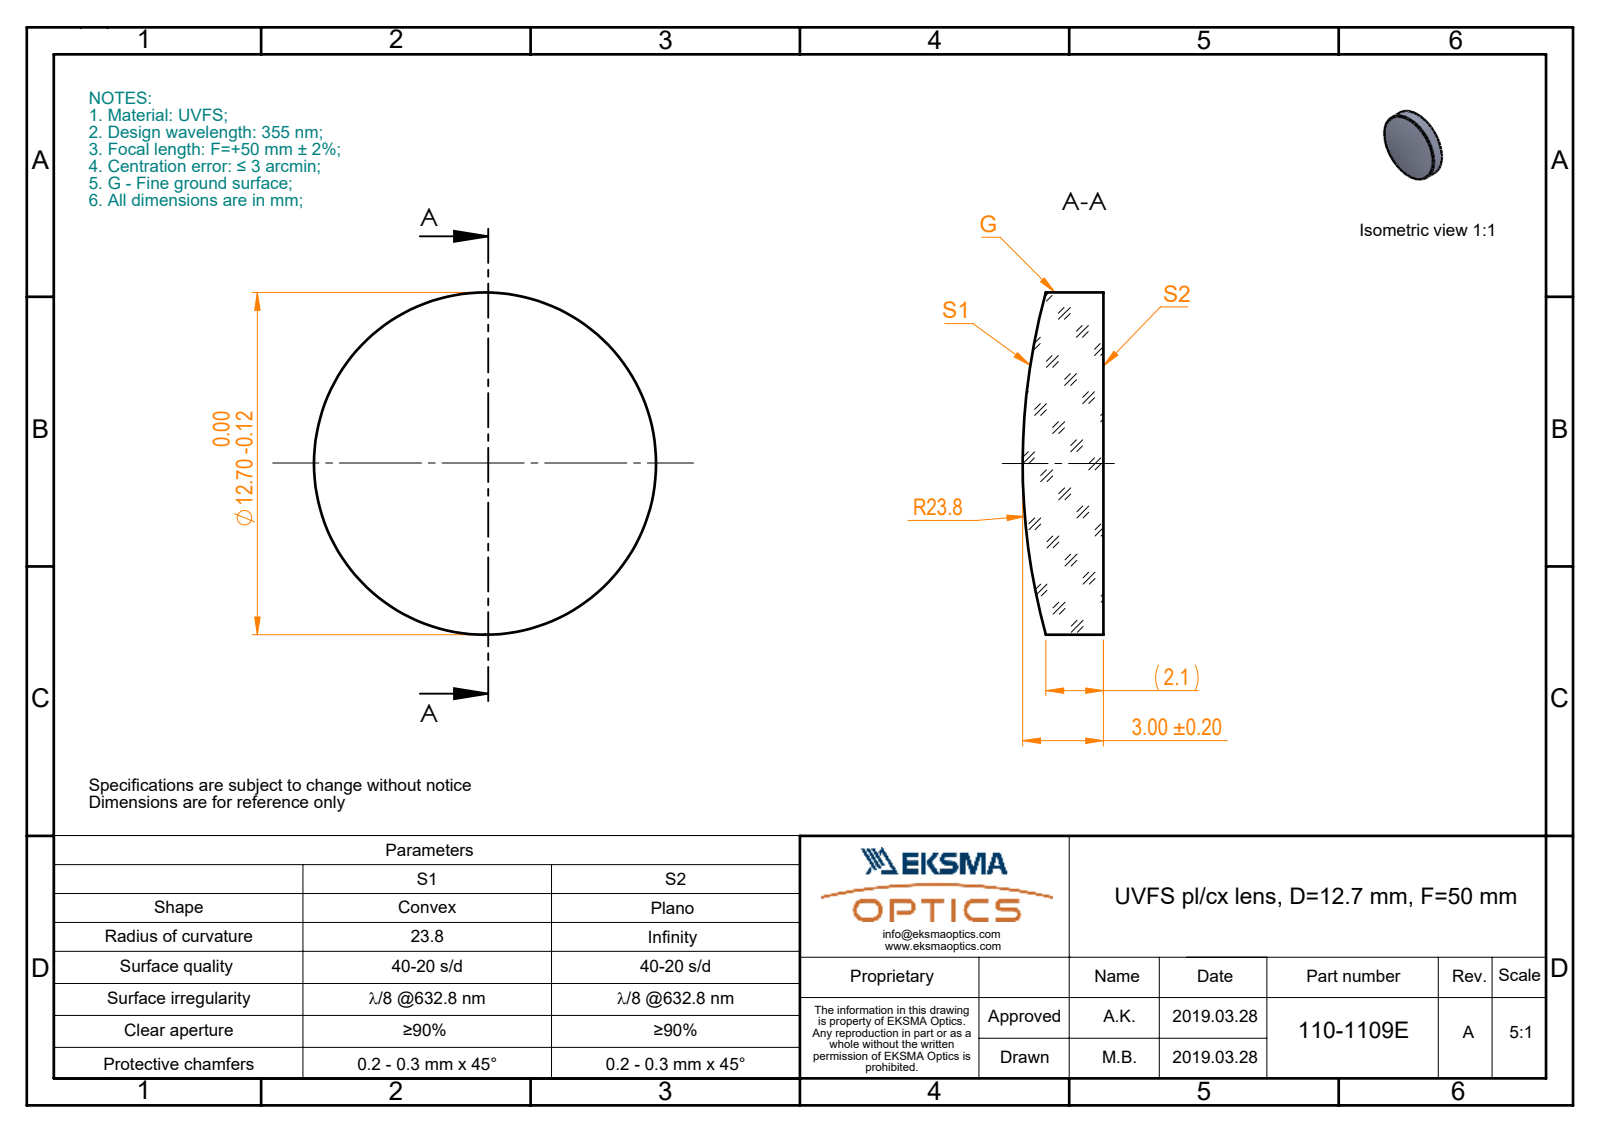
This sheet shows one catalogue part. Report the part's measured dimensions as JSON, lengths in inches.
{"part_name": "110-1109E UVFS pl-cx 12.7 F50", "step_written_by": "SolidWorks 2017 (CONFIG_CONTROL_DESIGN)", "units": "inches", "bodies": {"solids": 1, "faces": 5, "planar": 1, "cylindrical": 2, "other": 2}, "overall_size": [0.5, 0.5, 0.118], "volume_in3": 0.02, "surface_area_in2": 0.529, "round_bosses_or_shafts": [[0.5, 1]]}
